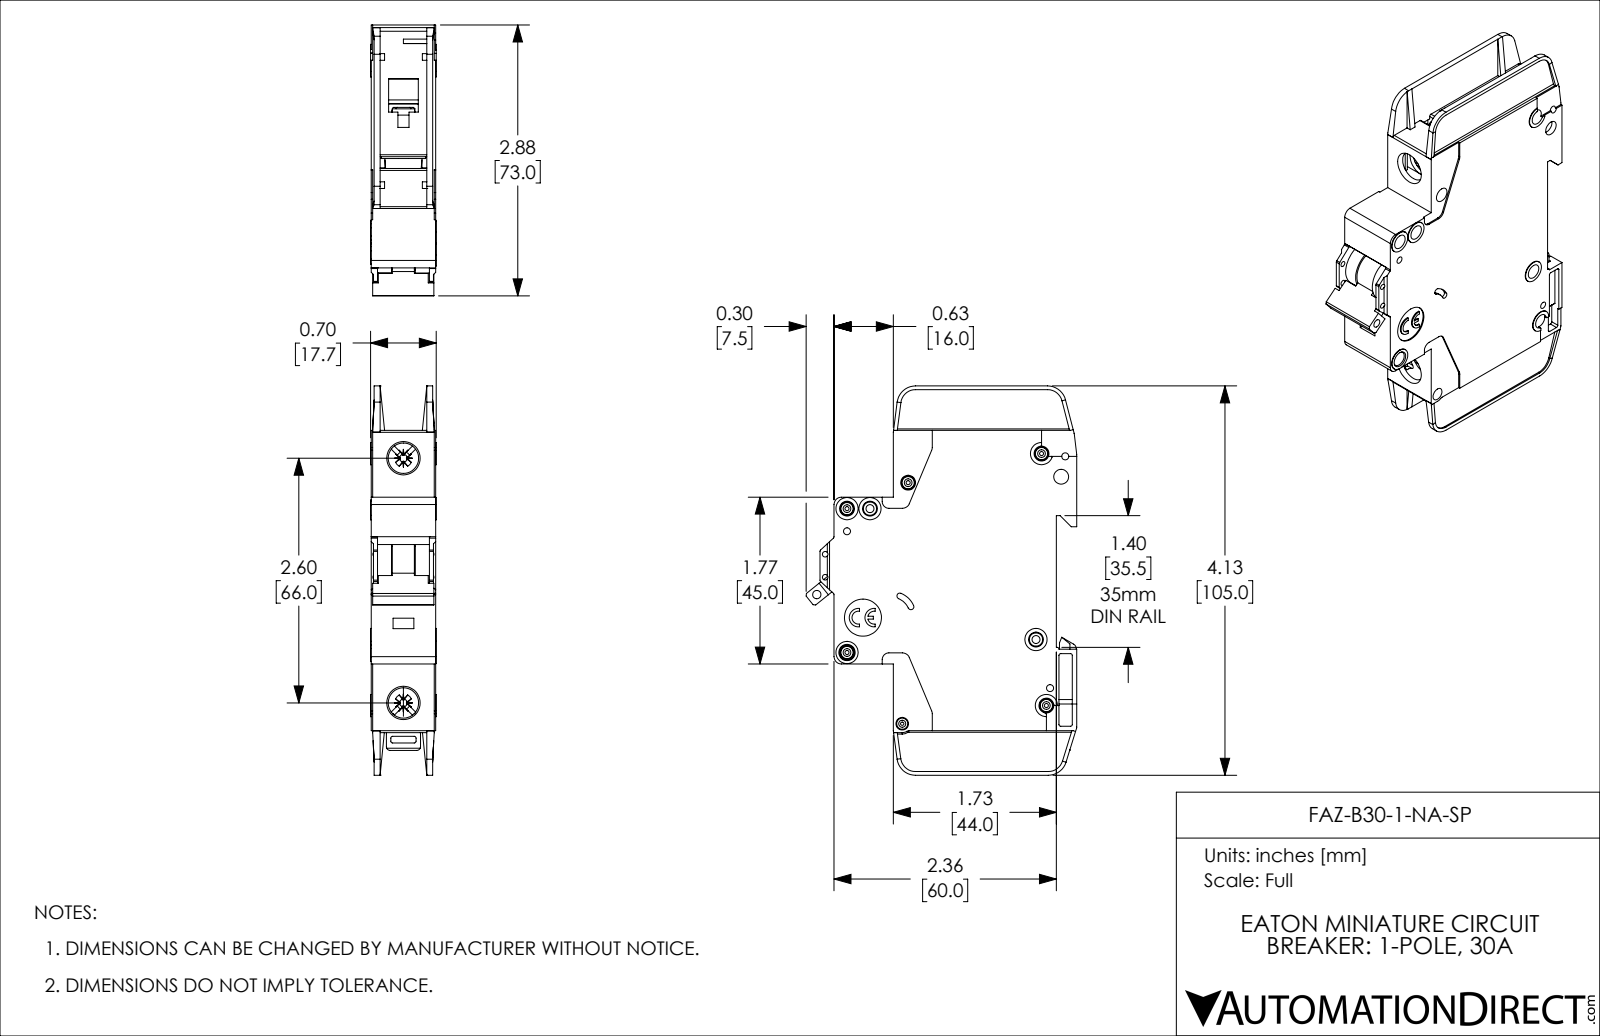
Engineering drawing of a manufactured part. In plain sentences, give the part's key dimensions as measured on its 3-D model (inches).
The part is named "FAZ-B30-1-NA-SP". Its 3-D file was written by "SolidWorks 2019 (AUTOMOTIVE_DESIGN)". It is 1 solid with 1127 faces: 671 planar, 357 cylindrical and 99 other. Overall it measures 4.134 by 2.876 by 0.697 inches. Its volume is 4.682 cubic inches and its surface area 41.01 square inches. Round holes: 8 of diameter 0.157, 5 of diameter 0.043, 4 of diameter 0.075, 2 of diameter 0.059, 2 of diameter 0.085, 2 of diameter 0.323, 1 of diameter 0.035, 1 of diameter 0.089, 1 of diameter 0.098, 1 of diameter 0.134, 1 of diameter 0.394. Round bosses or shafts: 5 of diameter 0.13, 4 of diameter 0.236, 2 of diameter 0.118, 1 of diameter 0.098. Partial cylindrical surfaces (rounded edges, fillets, slot ends): 42 of radius 0.02, 10 of radius 0.016, 10 of radius 0.039, 8 of radius 0.079, 5 of radius 0.197, 4 of radius 0.008, 4 of radius 0.026, 4 of radius 0.043. The main face-to-face distances are 0.047, 0.685, 0.591, 0.638, 0.094, 0.543, 0.016, 0.031, 0.496, 0.575. The hole center spacings are 0.244, 0.537, 0.87, 0.189, 0.199, 0.204, 0.221, 0.24.
